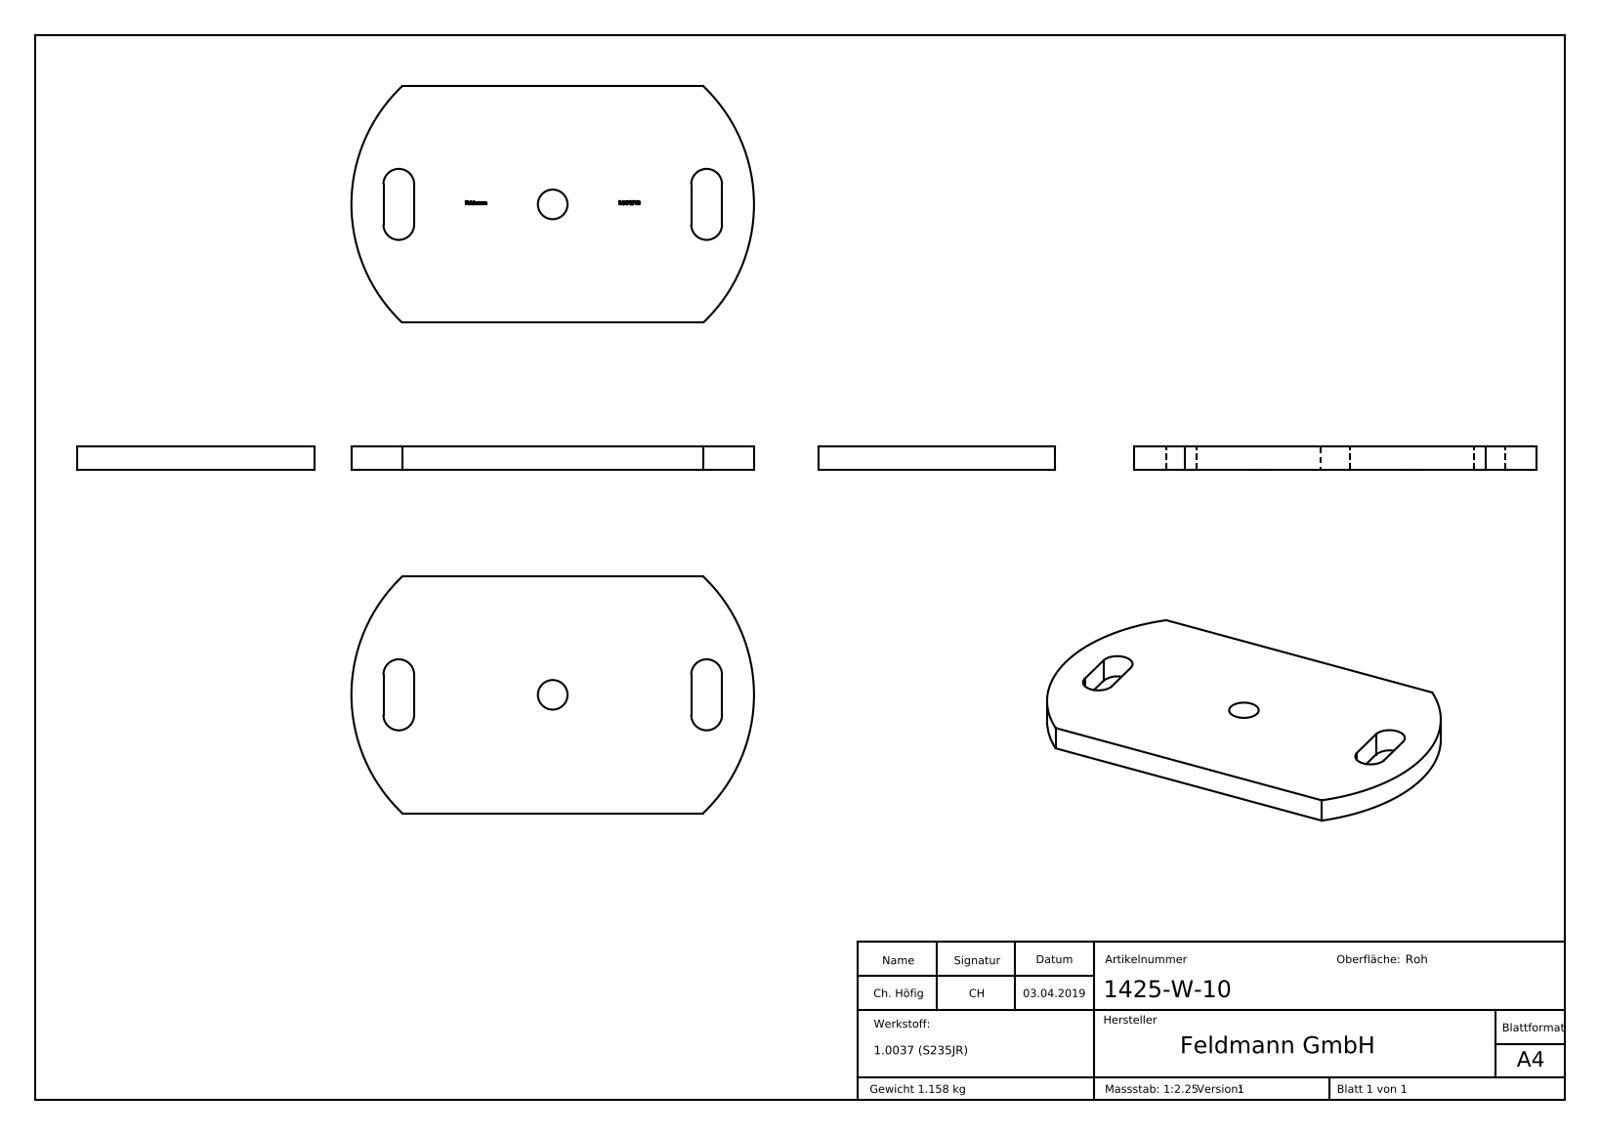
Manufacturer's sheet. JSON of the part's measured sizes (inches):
{"part_name": "1425-W-10", "step_written_by": "SolidWorks 2015 (CONFIG_CONTROL_DESIGN)", "units": "inches", "bodies": {"solids": 1, "faces": 223, "planar": 142, "cylindrical": 10, "other": 71}, "overall_size": [6.693, 3.937, 0.394], "volume_in3": 9.056, "surface_area_in2": 56.35, "round_holes": [[0.492, 1]], "partial_cylinders_radius": [[0.256, 4], [2.712, 2]], "face_to_face_distances": [0.394, 3.937, 0.512, 5.118, 5.63, 4.606, 0.39, 1.969, 2.479, 2.754]}
